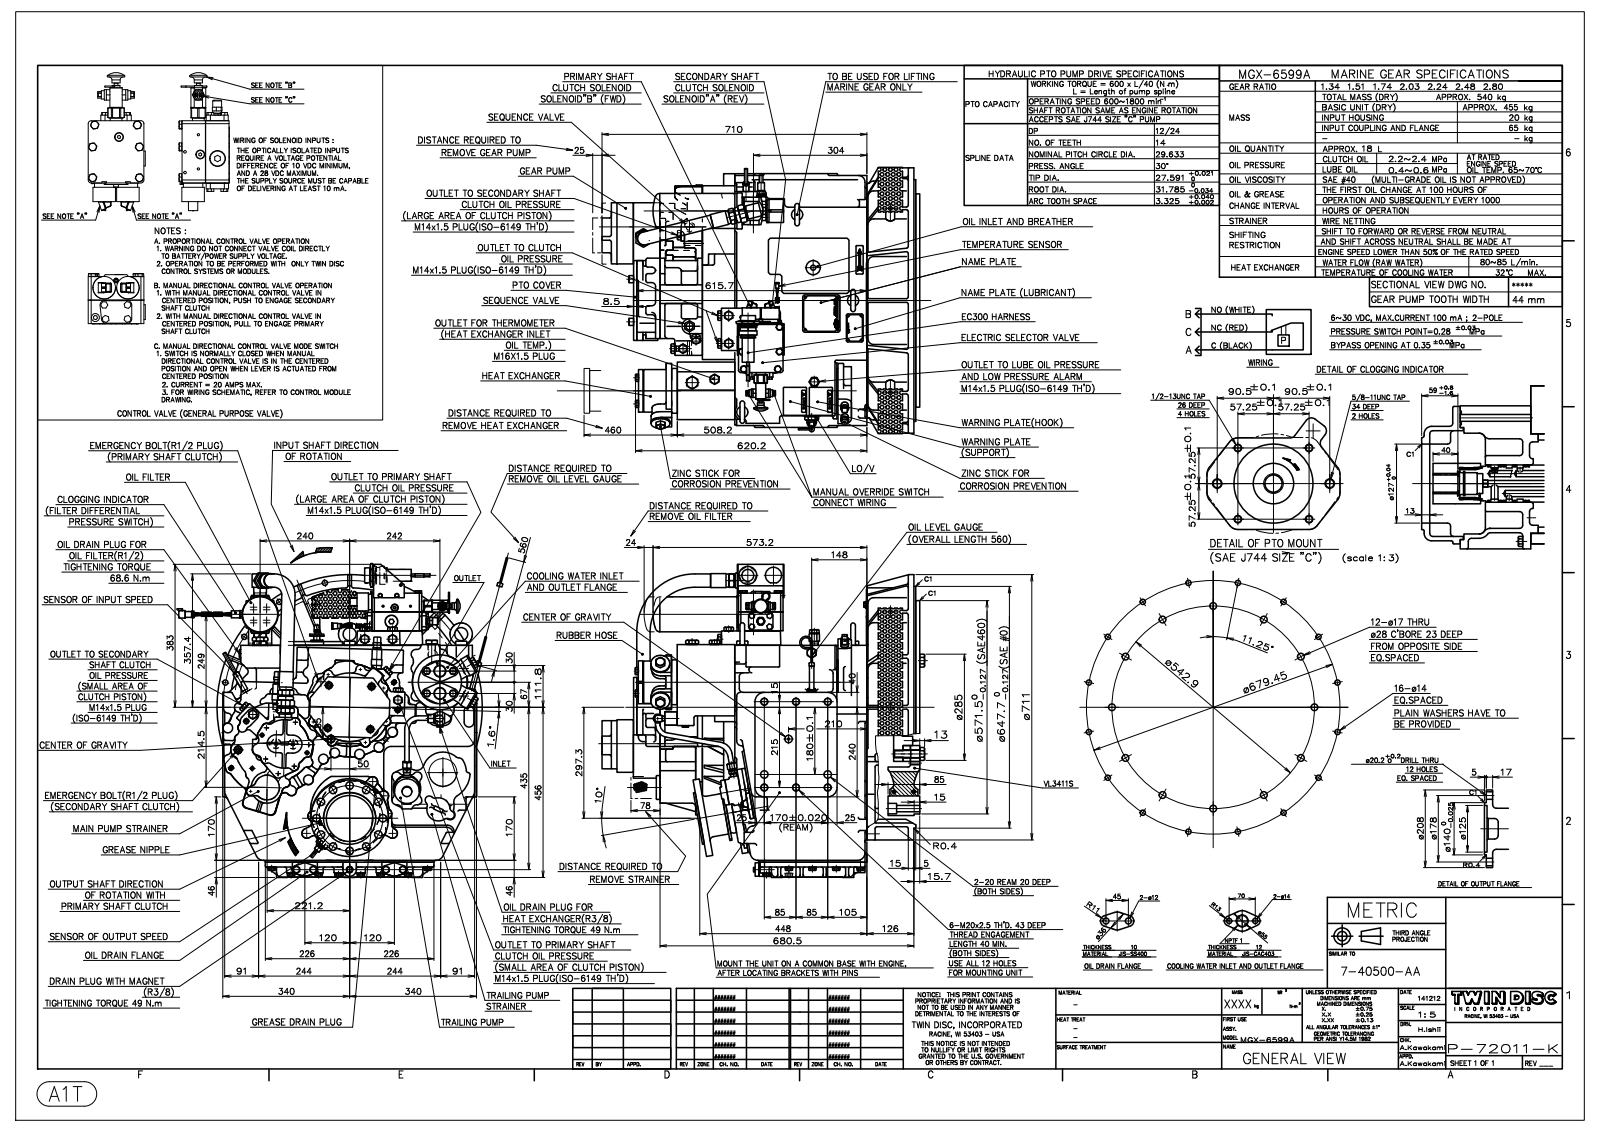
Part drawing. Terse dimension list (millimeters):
name: P72011K
written by: SolidWorks 2013 (AUTOMOTIVE_DESIGN)
unit: mm
bodies: 0 solids, 5078 faces (1813 planar, 2051 cylindrical, 1214 other)
size: 864.7 × 839.14 × 713.4
holes: 52× ⌀10, 16× ⌀14, 12× ⌀12, 12× ⌀17, 12× ⌀20.3, 8× ⌀20, 7× ⌀8, 6× ⌀30.5, 4× ⌀10.58, 4× ⌀30, 3× ⌀19, 3× ⌀35
bosses: 16× ⌀12, 9× ⌀30, 7× ⌀26, 6× ⌀18, 5× ⌀33, 5× ⌀22, 4× ⌀15.7, 4× ⌀10
rounds: 218× R10, 100× R12, 77× R5, 75× R13, 53× R3, 51× R2, 36× R20, 24× R50
face distances: 5, 141.7, 10, 349, 354, 13, 61.7, 80, 495.7, 410.7
hole spacings: 339.72, 89, 46.07, 132.55, 339.73, 377.48, 480.44, 564.94
